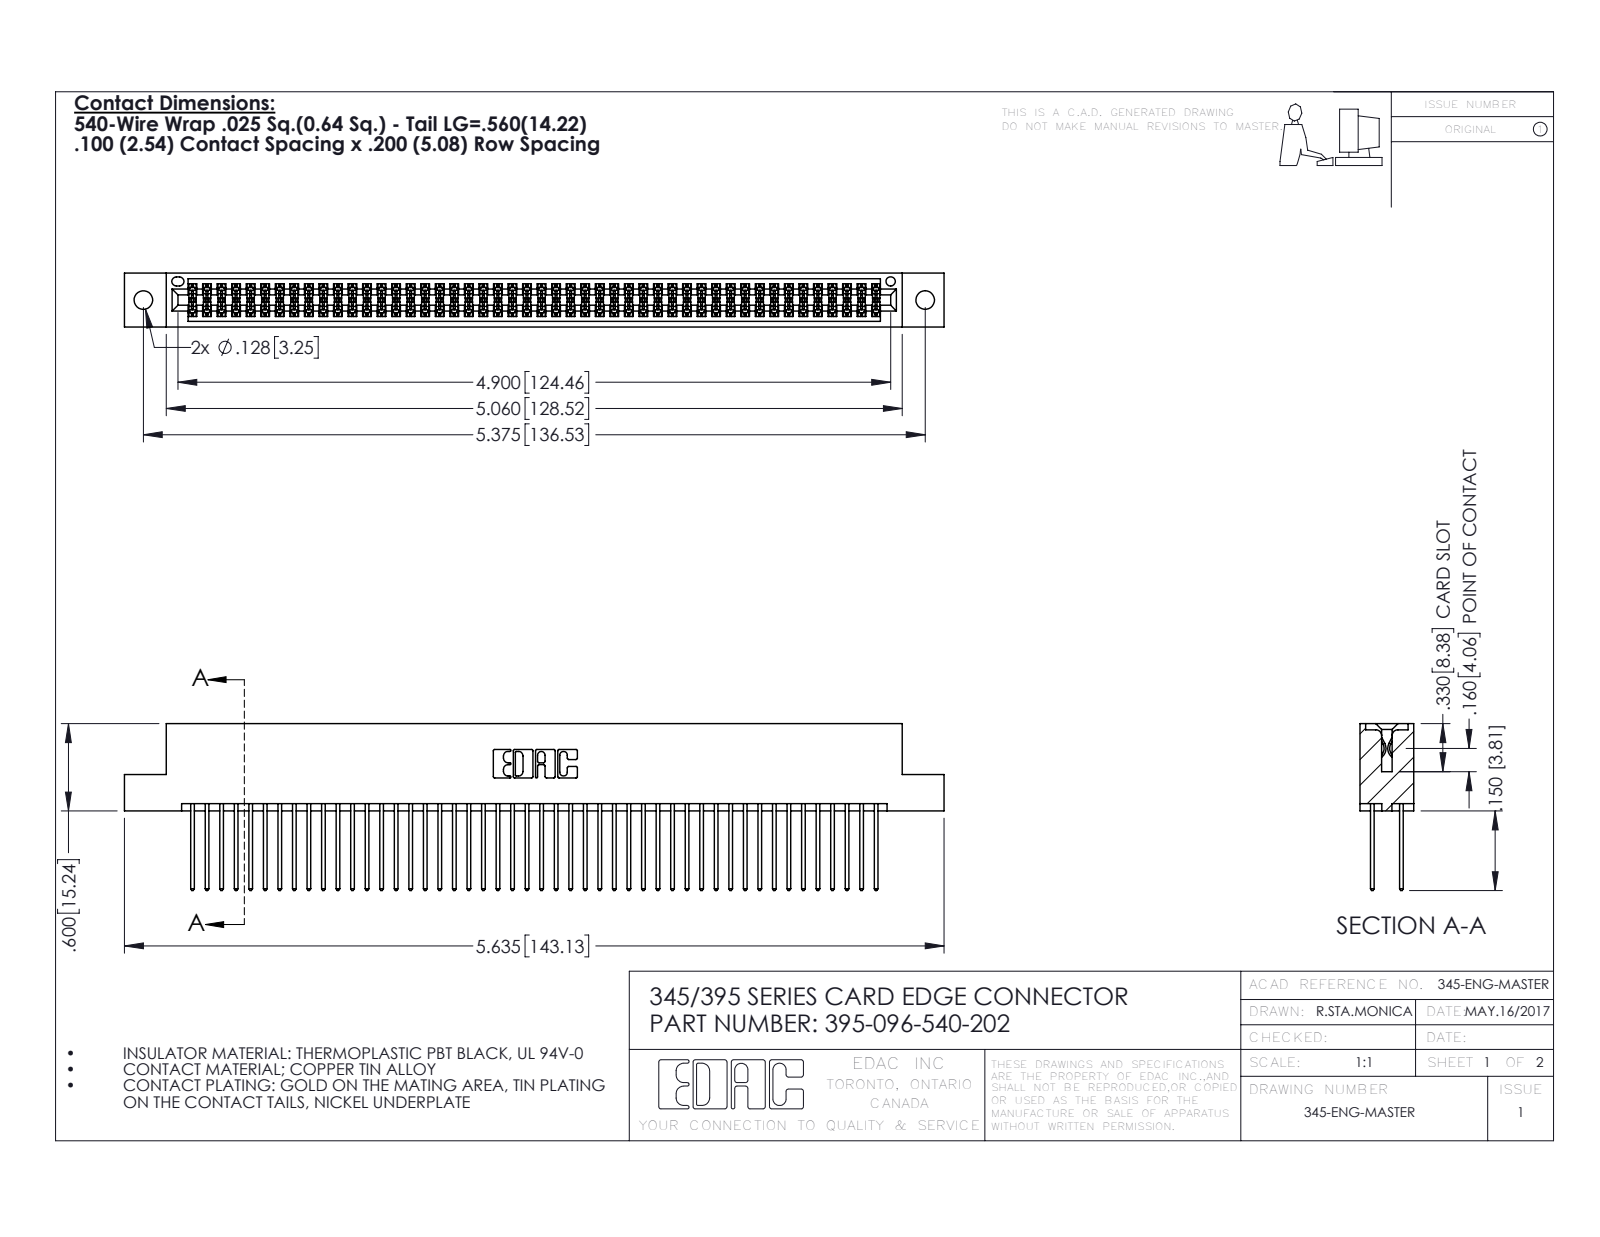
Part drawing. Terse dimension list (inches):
name: 345 Part_Flush Mounting Lugs - 0.128 Dia; 395-096-540-202; 345-292-001_345-293-140
written by: SolidWorks 2016 (CONFIG_CONTROL_DESIGN)
unit: in
bodies: 97 solids, 4926 faces (3248 planar, 1678 cylindrical, 0 other)
size: 5.635 × 1.147 × 0.37
volume: 0.872 in³; area: 35.11 in²
holes: 2× ⌀0.128, 1× ⌀0.064
rounds: 144× R0.006, 96× R0.01, 22× R0.01, 6× R0.007, 6× R0.031, 3× R0.026, 2× R0.014, 2× R0.019
face distances: 0.298, 0.072, 0.2, 0.098, 0.272, 0.025, 0.37, 0.225, 0.175, 0.149
hole spacings: 0.27, 5.139, 5.375
